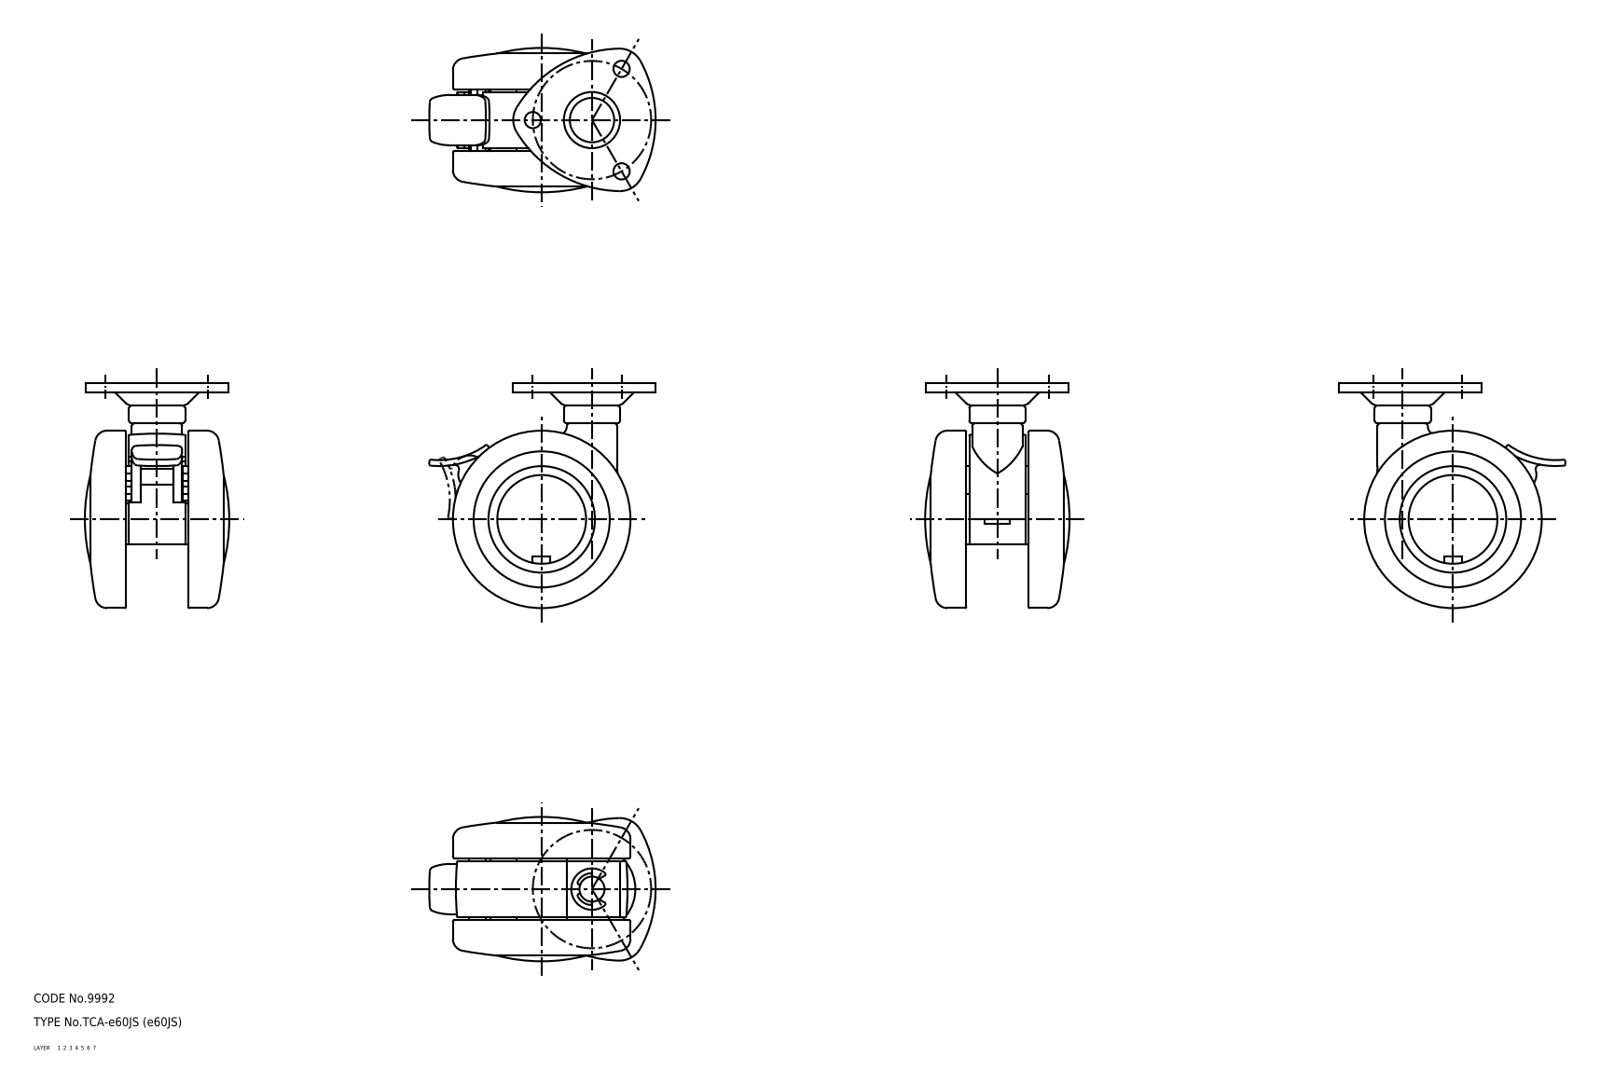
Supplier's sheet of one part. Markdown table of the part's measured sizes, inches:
| quantity | value |
| --- | --- |
| part name | wheel_mr; wheel; mounting plate; main shaft (+2 more) |
| STEP written by | CADfix (AUTOMOTIVE_DESIGN) |
| units | inches |
| bodies | 6 solids, 231 faces (0 planar, 0 cylindrical, 231 other) |
| overall size | 3.012 × 2.992 × 1.922 |
| volume | 5.596 in³ |
| surface area | 57.04 in² |
